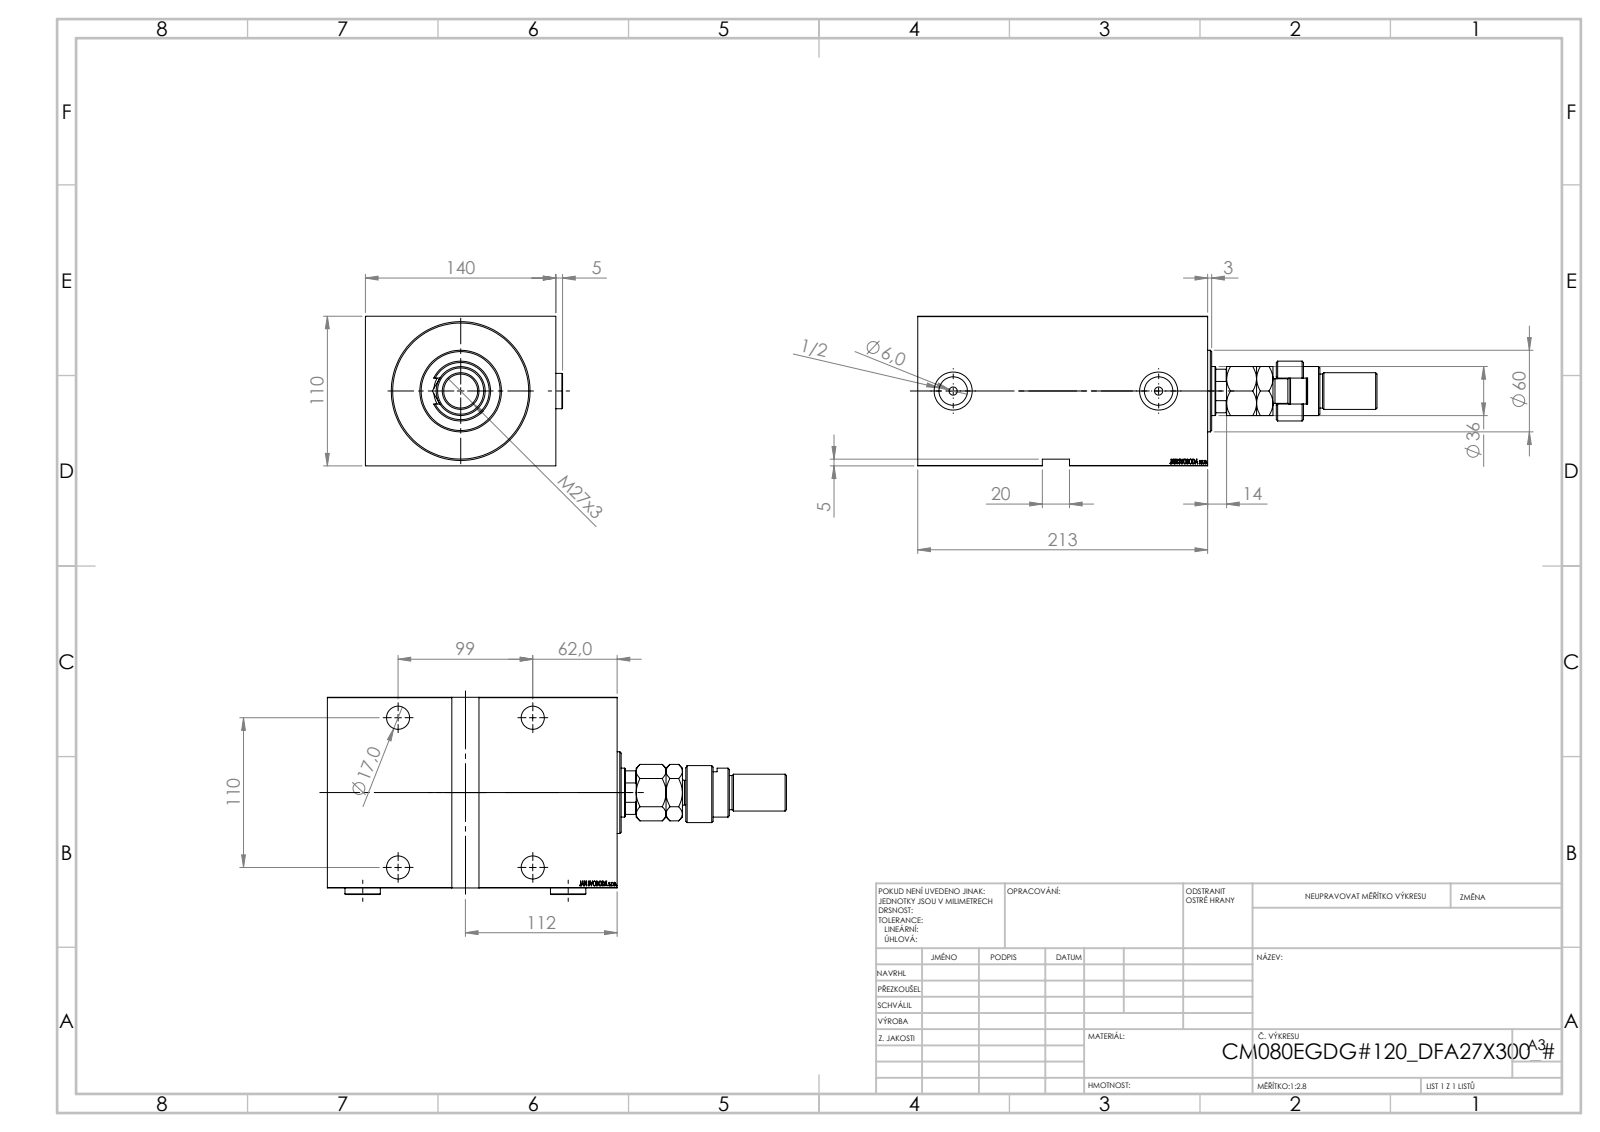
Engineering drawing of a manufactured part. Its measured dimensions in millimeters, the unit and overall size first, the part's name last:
Units: millimetres
Overall size (bounding box): 337.5 × 144.9 × 110
Round holes (diameter × count): ⌀17 ×4, ⌀25 ×4, ⌀6 ×2, ⌀20.96 ×2, ⌀28 ×2, ⌀25.5 ×1, ⌀39.5 ×1, ⌀80 ×1, ⌀100 ×1
Round bosses / shafts (diameter × count): ⌀26 ×2, ⌀82 ×1, ⌀60 ×1, ⌀44 ×1, ⌀36 ×1, ⌀28 ×1, ⌀27 ×1, ⌀25 ×1
Partial cylindrical surfaces — rounded edges, fillets, slot ends (radius × count): R9.5 ×1, R15 ×1, R17.5 ×1
Main face-to-face distances: 110, 140, 213, 192, 21, 5, 208, 187, 79, 196.4
Hole centre spacings: 99, 110, 147.99, 151
Volume: 2 756 000 mm³ · Surface area: 304 483 mm²
Bodies: 7 solids, 997 faces (474 planar, 81 cylindrical, 442 other)
Part name (STEP PRODUCT): V450CM_E_Body; MFA; FEMALE_PART_FOR_DFA; V450CM_E_VCP (+2 more)
STEP written by: SolidWorks 2019 (CONFIG_CONTROL_DESIGN)
